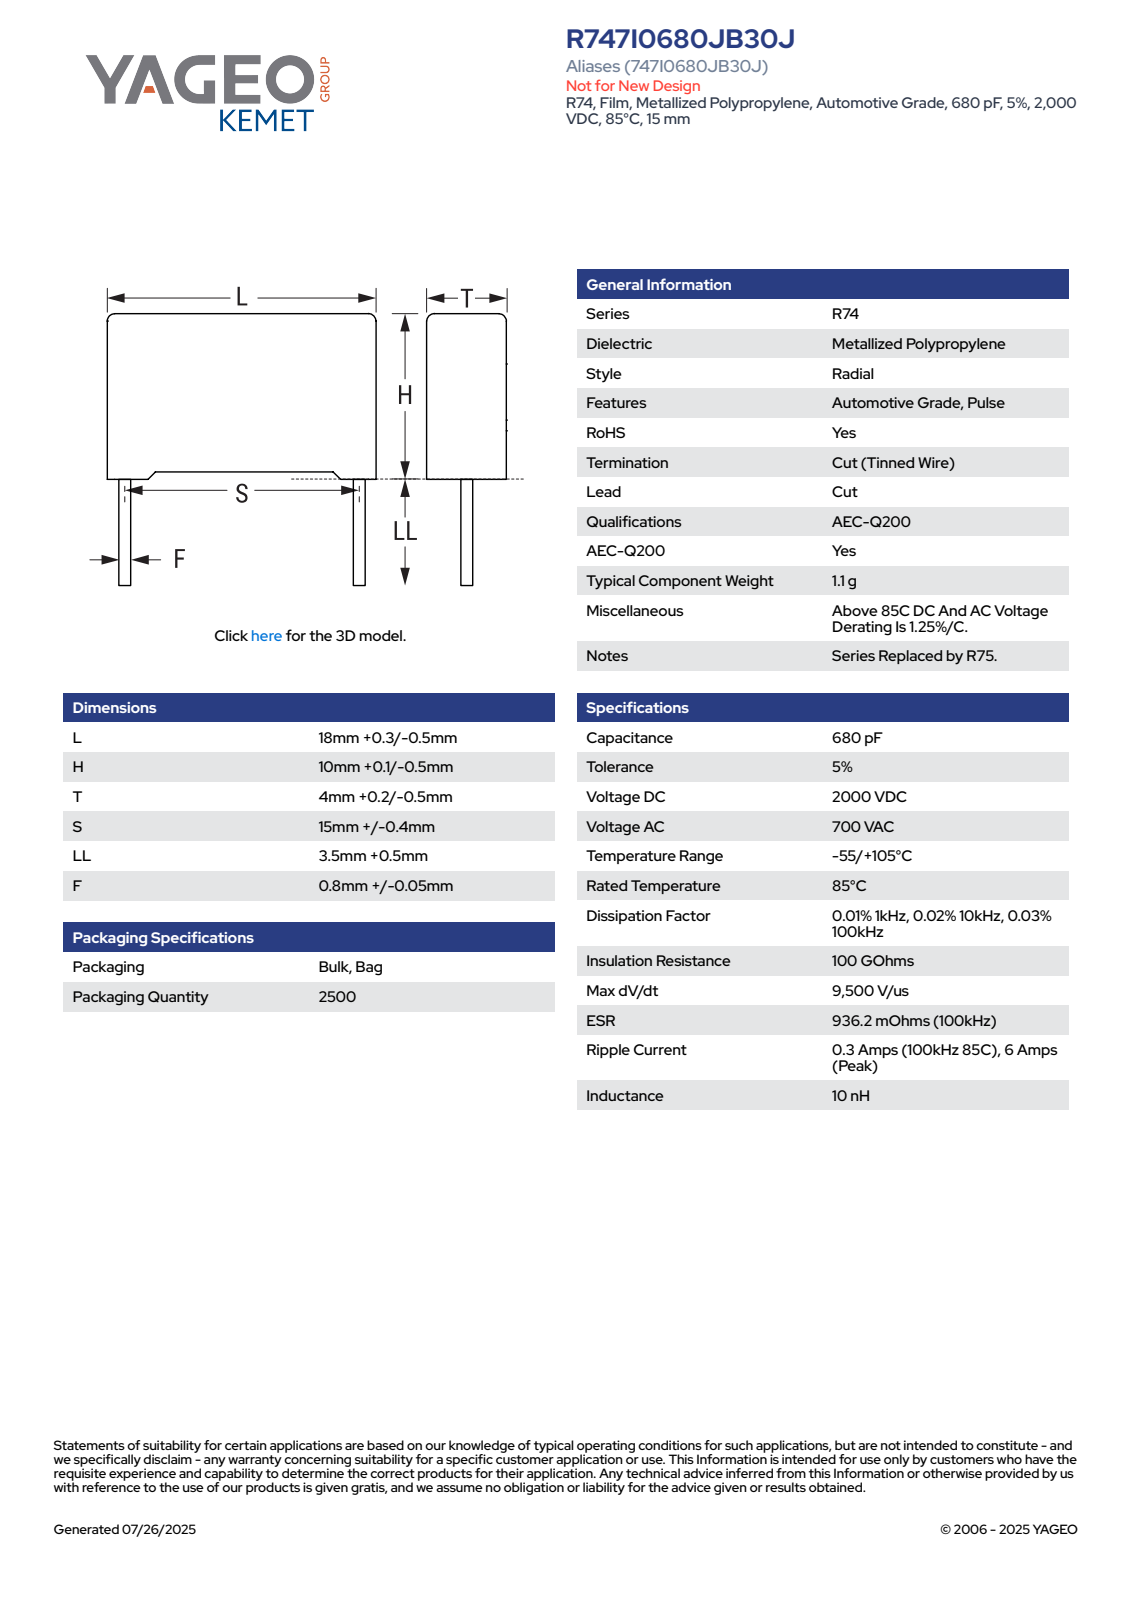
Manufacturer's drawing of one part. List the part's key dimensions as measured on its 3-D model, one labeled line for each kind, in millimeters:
Part name (STEP PRODUCT): CFR_RB2_18X10X4_L18.3H10.1T4.2S15LL4F0.85
STEP written by: SolidWorks 2021 (AUTOMOTIVE_DESIGN)
Units: millimetres
Bodies: 4 solids, 85 faces (77 planar, 8 cylindrical, 0 other)
Overall size (bounding box): 18.3 × 14.1 × 4.21
Volume: 736 mm³ · Surface area: 663 mm²
Round bosses / shafts (diameter × count): ⌀0.85 ×2
Partial cylindrical surfaces — rounded edges, fillets, slot ends (radius × count): R0.5 ×4
Main face-to-face distances: 4.2, 9.35, 18.3, 0.61, 3.59, 0.4, 9.75, 0.75, 0.35, 10.1
